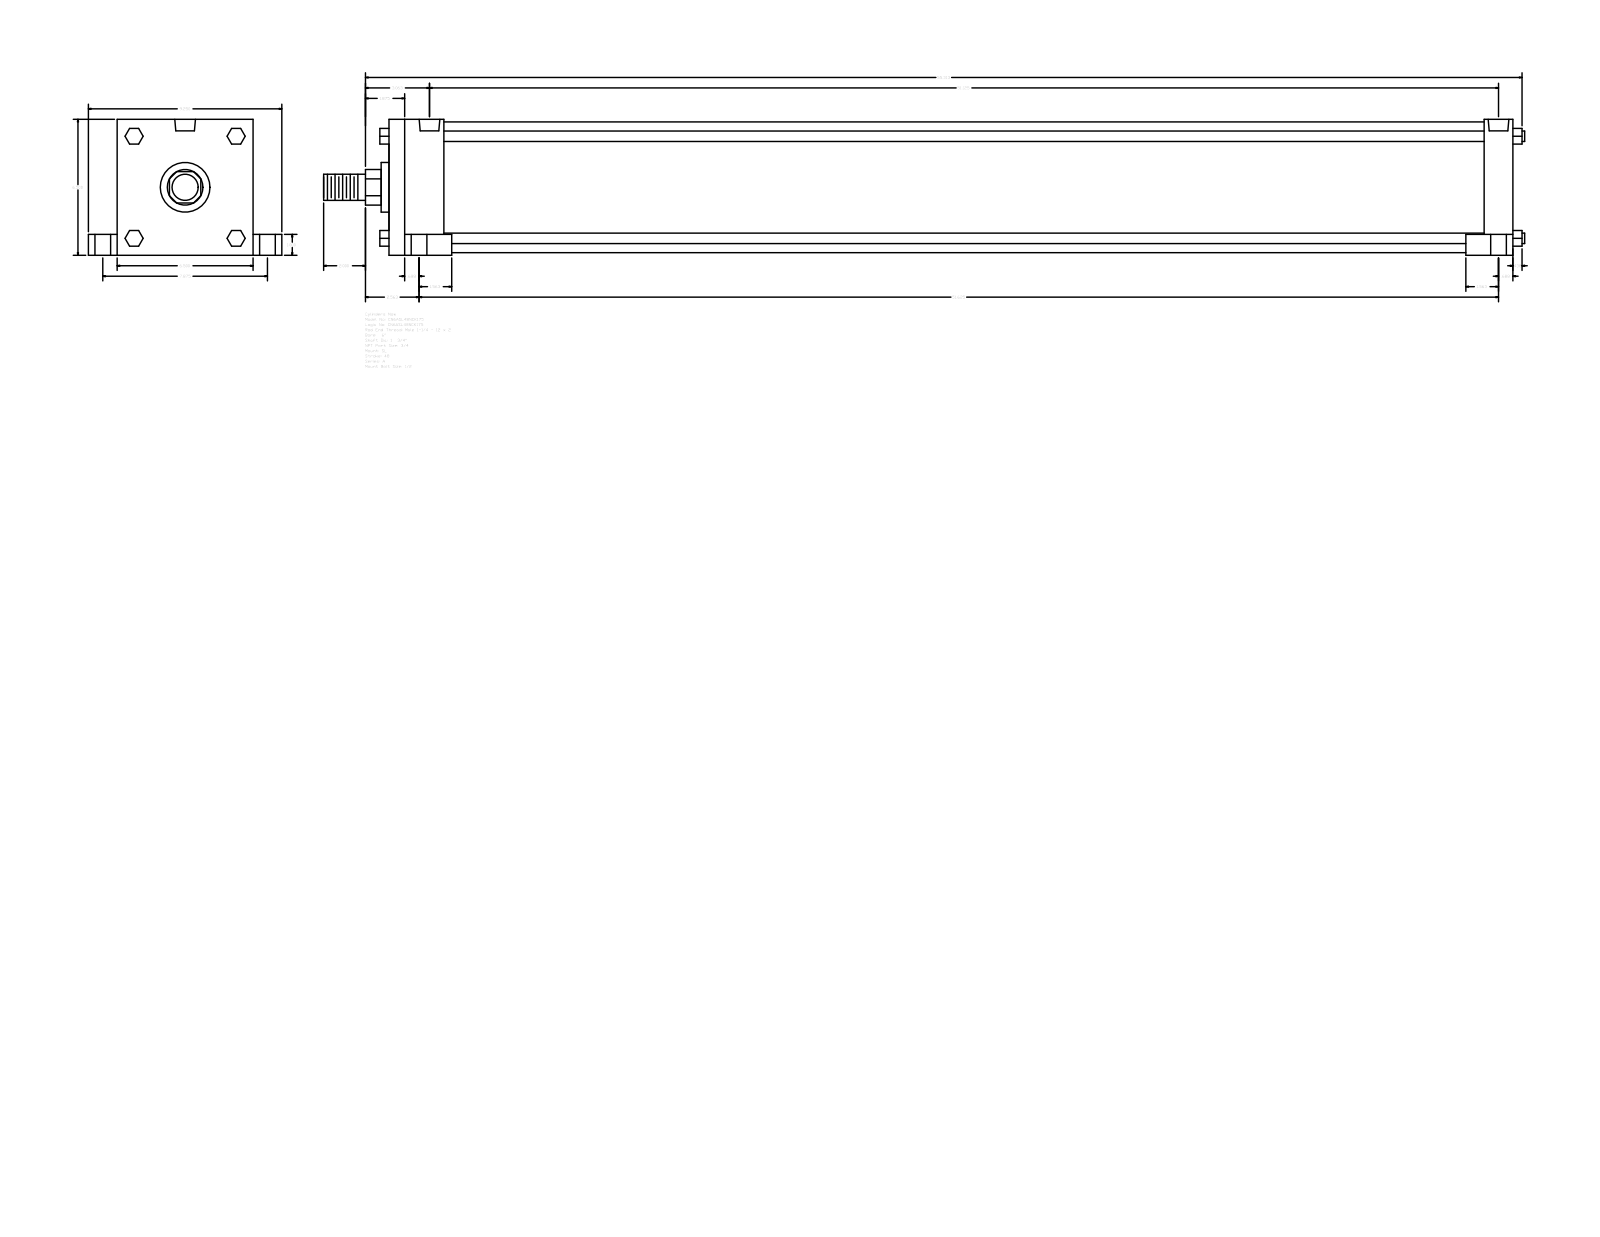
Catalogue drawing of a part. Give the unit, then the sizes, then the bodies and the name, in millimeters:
Units: millimetres
Overall size (bounding box): 1458.91 × 234.95 × 165.1
Round holes (diameter × count): ⌀15.08 ×4, ⌀19.05 ×4, ⌀25.4 ×4, ⌀25.12 ×2
Round bosses / shafts (diameter × count): ⌀12.7 ×4, ⌀158.75 ×1, ⌀60.33 ×1, ⌀44.45 ×1, ⌀31.75 ×1
Partial cylindrical surfaces — rounded edges, fillets, slot ends (radius × count): R21.63 ×1
Main face-to-face distances: 165.1, 1365.26, 66.68, 1298.58, 1330.33, 1263.65, 34.93, 25.4, 139.7, 34.92
Hole centre spacings: 5.56, 100.01, 100.16, 100.81, 101.66, 200.02, 1287.45, 1293.01
Bodies: 0 solids, 150 faces (114 planar, 36 cylindrical, 0 other)
Part name (STEP PRODUCT): A_SL__0600_1.75
STEP written by: GSSL Pune (CONFIG_CONTROL_DESIGN)
